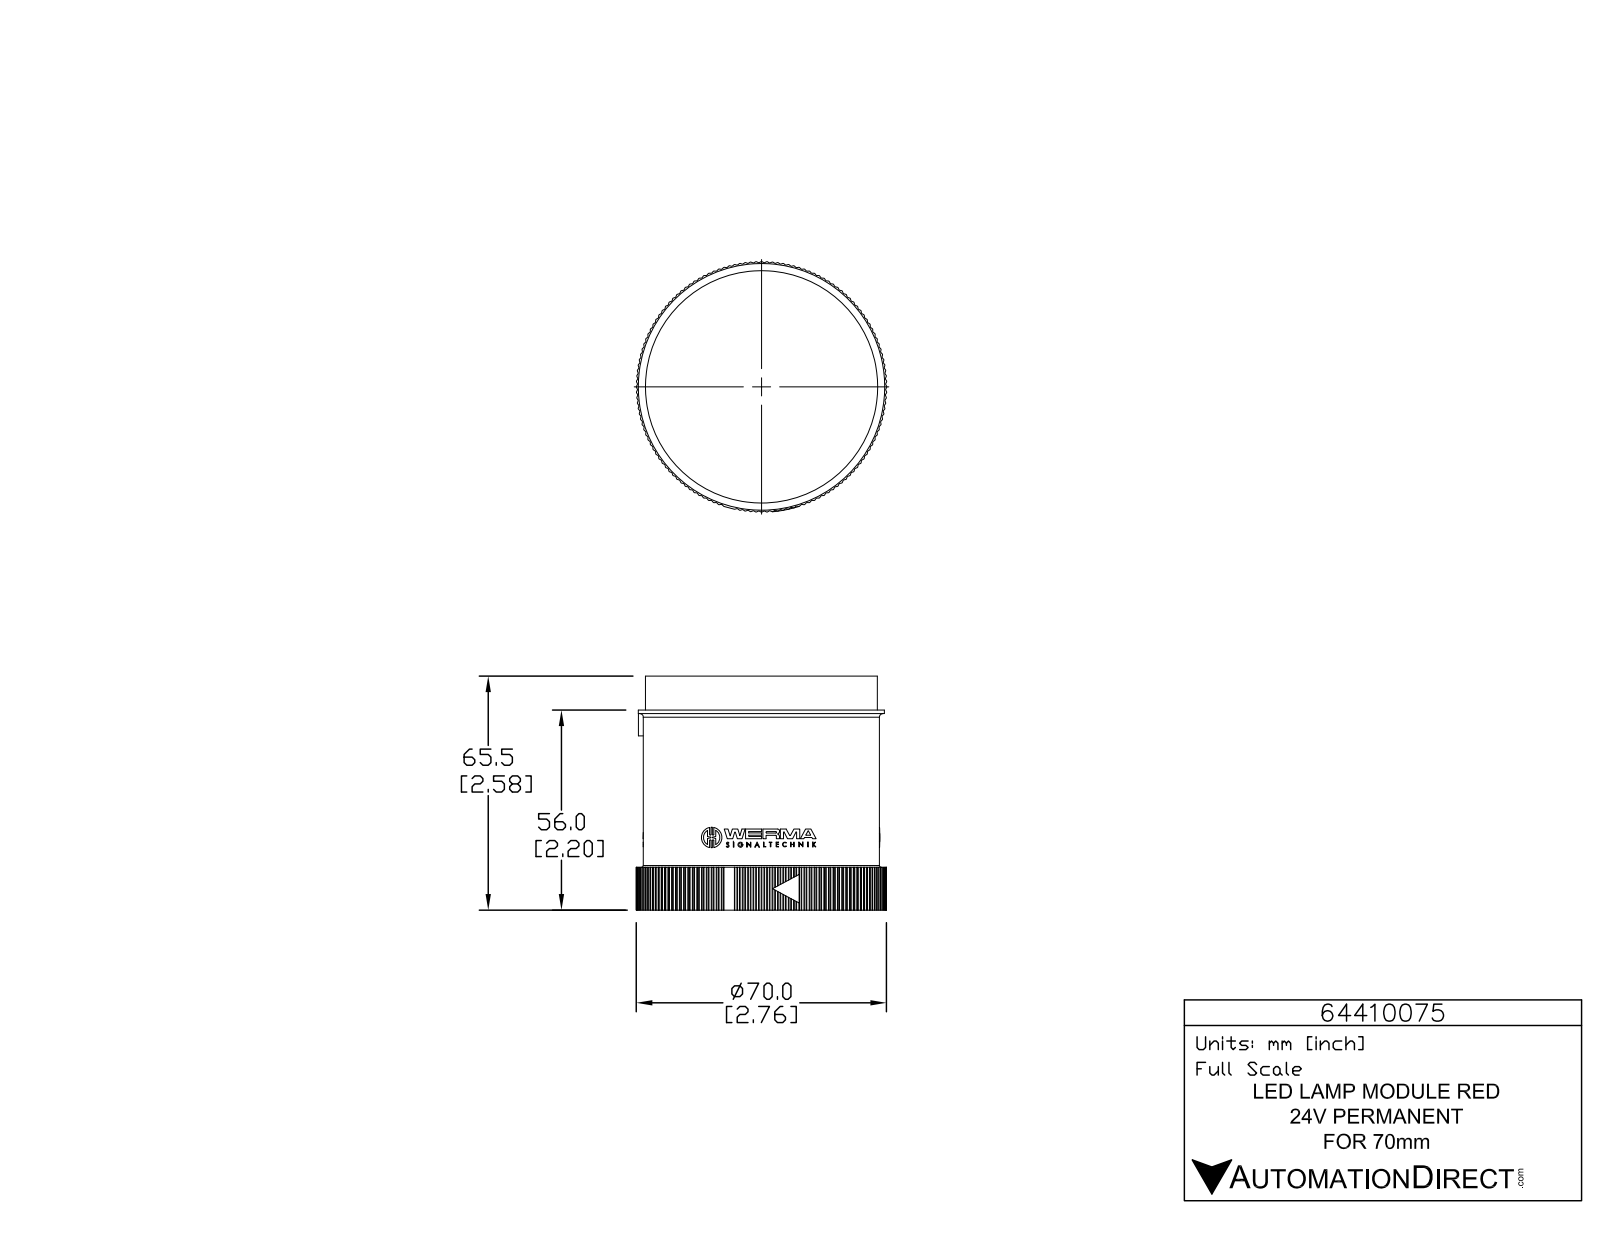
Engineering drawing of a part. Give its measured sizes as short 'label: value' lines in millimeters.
name: 64410075
written by: SolidWorks 2015 (AUTOMOTIVE_DESIGN)
unit: mm
bodies: 1 solid, 1400 faces (832 planar, 563 cylindrical, 5 other)
size: 70.2 × 70.2 × 65.5
volume: 197 000 mm³; area: 24 180 mm²
holes: 3× ⌀1, 1× ⌀65.4
bosses: 3× ⌀5.7, 3× ⌀1.4, 1× ⌀69, 1× ⌀66.2, 1× ⌀65
rounds: 285× R0.2, 6× R0.2, 6× R0.2, 6× R0.2, 6× R3.3, 3× R0.1, 3× R0.1, 3× R0.2
face distances: 55.9, 62.3, 9.6, 65.5, 56, 46.4, 9.5, 62.3, 12, 2.4
